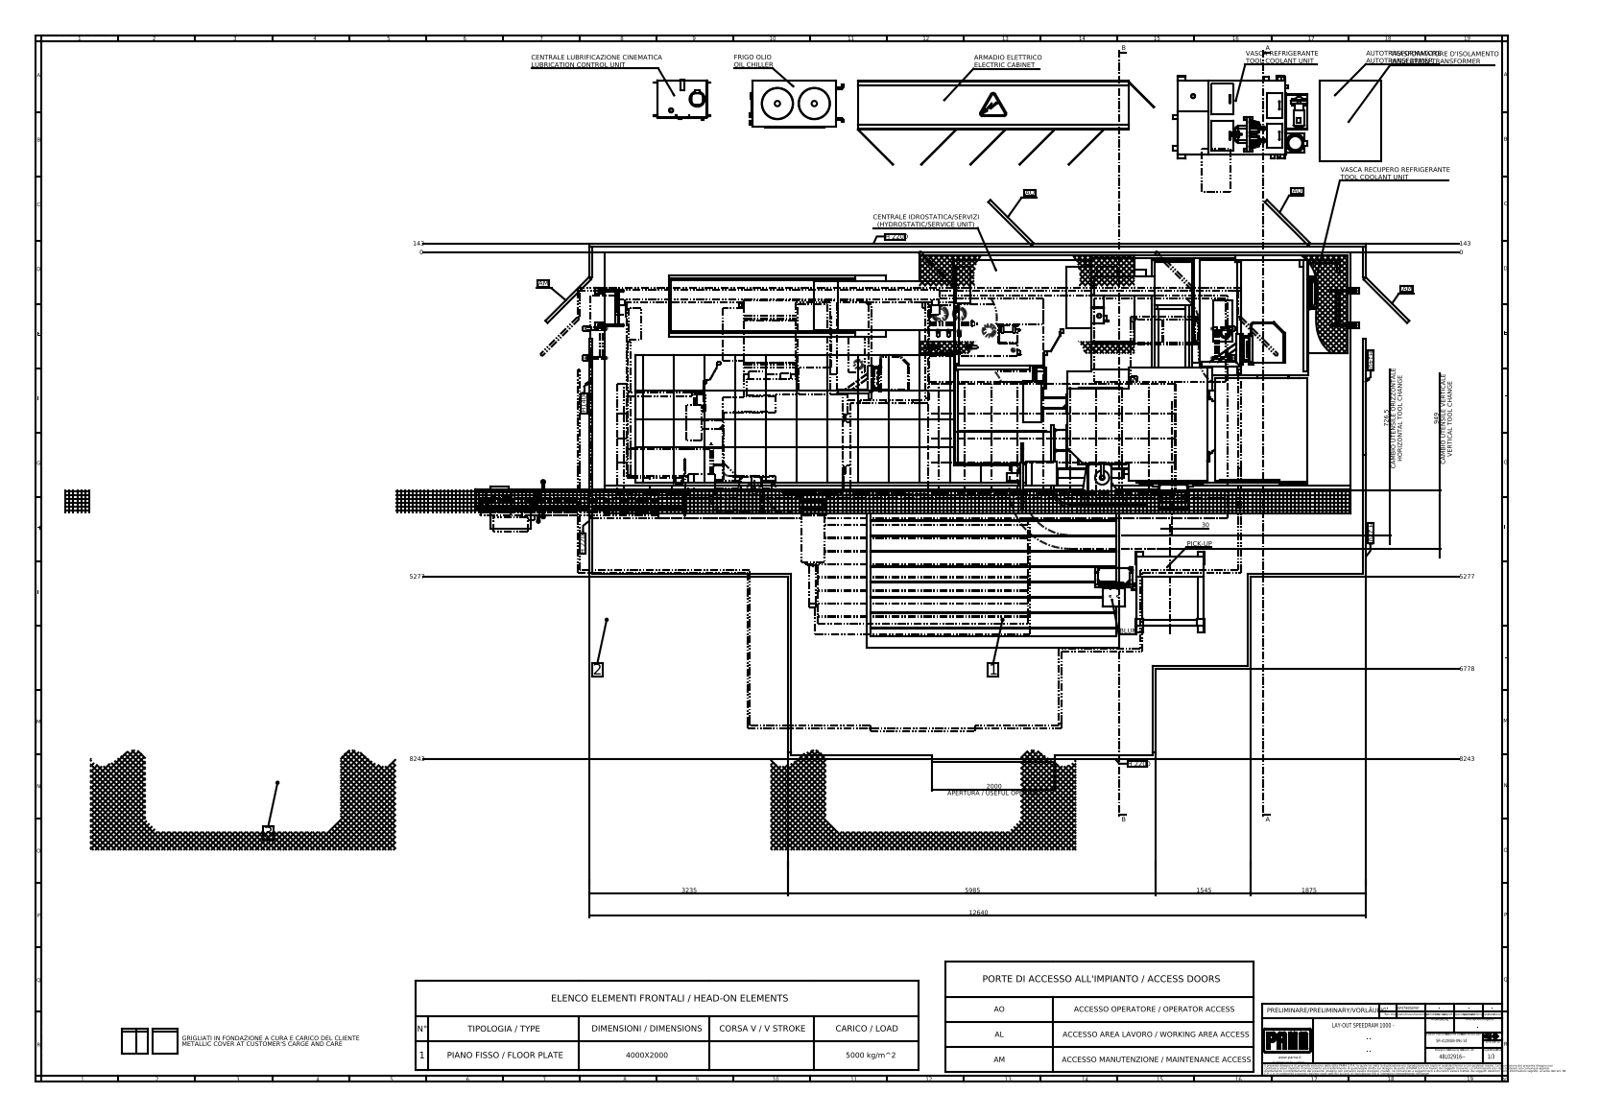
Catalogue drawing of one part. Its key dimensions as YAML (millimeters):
part_name: "S003226_BGB Ø130,4 W=800; S003207_X=5000; S003251_ISO 50 - RIPOSO; S000047 (+8 more)"
step_written_by: "SolidWorks 2023 (AUTOMOTIVE_DESIGN)"
units: millimeters
bodies: {solids: 402, faces: 6337, planar: 4451, cylindrical: 1432, other: 454}
overall_size: [16140, 14057.4, 7912.5]
volume: 415500000000
surface_area: 1636000000
round_holes:
  - {diameter: 35, count: 64}
  - {diameter: 69.6, count: 63}
  - {diameter: 37.2, count: 18}
  - {diameter: 30, count: 9}
  - {diameter: 13, count: 8}
  - {diameter: 14, count: 8}
  - {diameter: 8, count: 6}
  - {diameter: 12.5, count: 4}
  - {diameter: 56.66, count: 4}
  - {diameter: 60, count: 4}
  - {diameter: 25.6, count: 3}
  - {diameter: 50, count: 3}
round_bosses_or_shafts:
  - {diameter: 42.4, count: 18}
  - {diameter: 20, count: 14}
  - {diameter: 40, count: 11}
  - {diameter: 9, count: 10}
  - {diameter: 55, count: 8}
  - {diameter: 66.3, count: 7}
  - {diameter: 60, count: 6}
  - {diameter: 35, count: 6}
partial_cylinders:
  - {radius: 5, count: 128}
  - {radius: 15, count: 53}
  - {radius: 8, count: 52}
  - {radius: 35, count: 26}
  - {radius: 6, count: 25}
  - {radius: 3, count: 21}
  - {radius: 4, count: 21}
  - {radius: 10, count: 20}
face_to_face_distances: [2000, 50, 1247, 753, 5, 13986, 10, 16140, 2650, 2700]
hole_center_spacings: [273.13, 500, 1235.56, 758.02, 1423.59, 1000, 130, 260]
